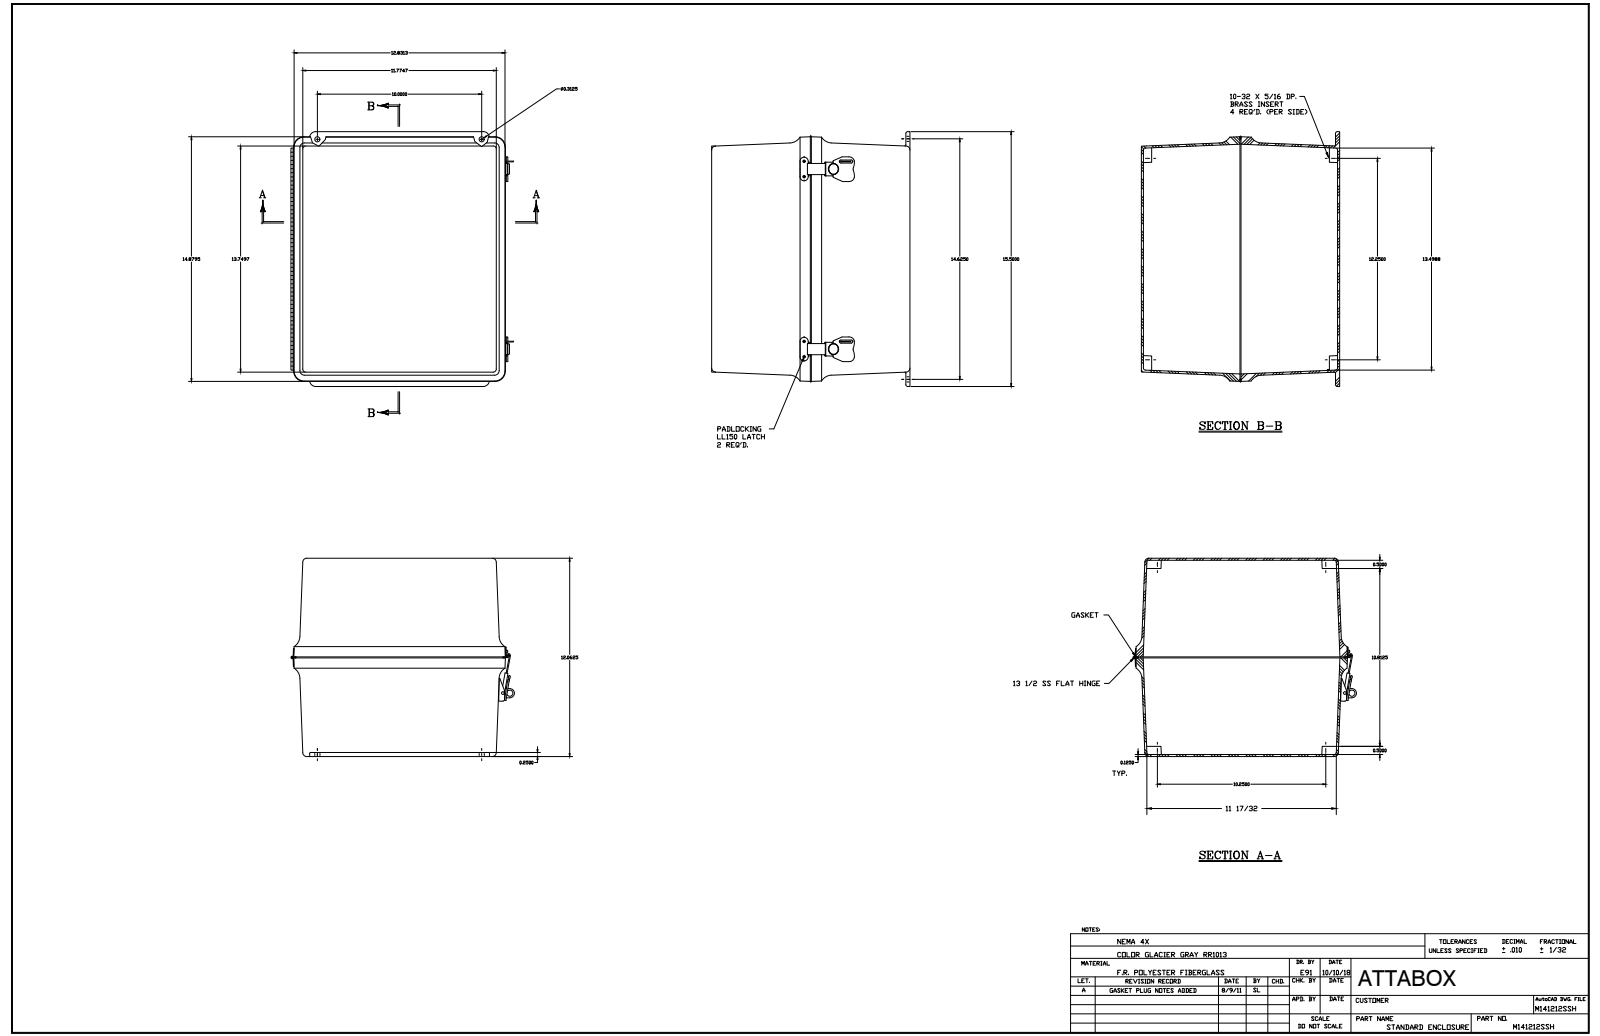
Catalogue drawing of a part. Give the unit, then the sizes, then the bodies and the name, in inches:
Units: inches
Overall size (bounding box): 15.5 × 13.553 × 12.056
Round holes (diameter × count): ⌀0.14 ×18, ⌀0.152 ×11, ⌀0.136 ×10, ⌀0.156 ×7, ⌀0.13 ×4, ⌀0.165 ×4, ⌀0.197 ×4, ⌀0.218 ×4, ⌀0.118 ×2, ⌀0.138 ×2, ⌀0.193 ×2, ⌀0.531 ×2
Round bosses / shafts (diameter × count): ⌀0.25 ×18, ⌀0.125 ×11, ⌀0.27 ×7, ⌀0.125 ×7, ⌀0.583 ×2, ⌀0.524 ×2, ⌀0.209 ×2, ⌀0.185 ×2
Partial cylindrical surfaces — rounded edges, fillets, slot ends (radius × count): R0.031 ×52, R0.079 ×19, R0.25 ×16, R0.75 ×14, R0.125 ×12, R0.037 ×8, R0.039 ×8, R0.045 ×8
Main face-to-face distances: 0.125, 0.125, 11.806, 11.959, 12.056, 11.93, 11.931, 13.957, 12.084, 12.084
Hole centre spacings: 3.25, 1.37, 6.5, 10.882, 11.26, 13.254, 15.972, 10.25
Volume: 151.1 in³ · Surface area: 2 059 in²
Bodies: 54 solids, 1459 faces (622 planar, 560 cylindrical, 277 other)
Part name (STEP PRODUCT): M141212SSH
STEP written by: SolidWorks 2018 (AUTOMOTIVE_DESIGN)
